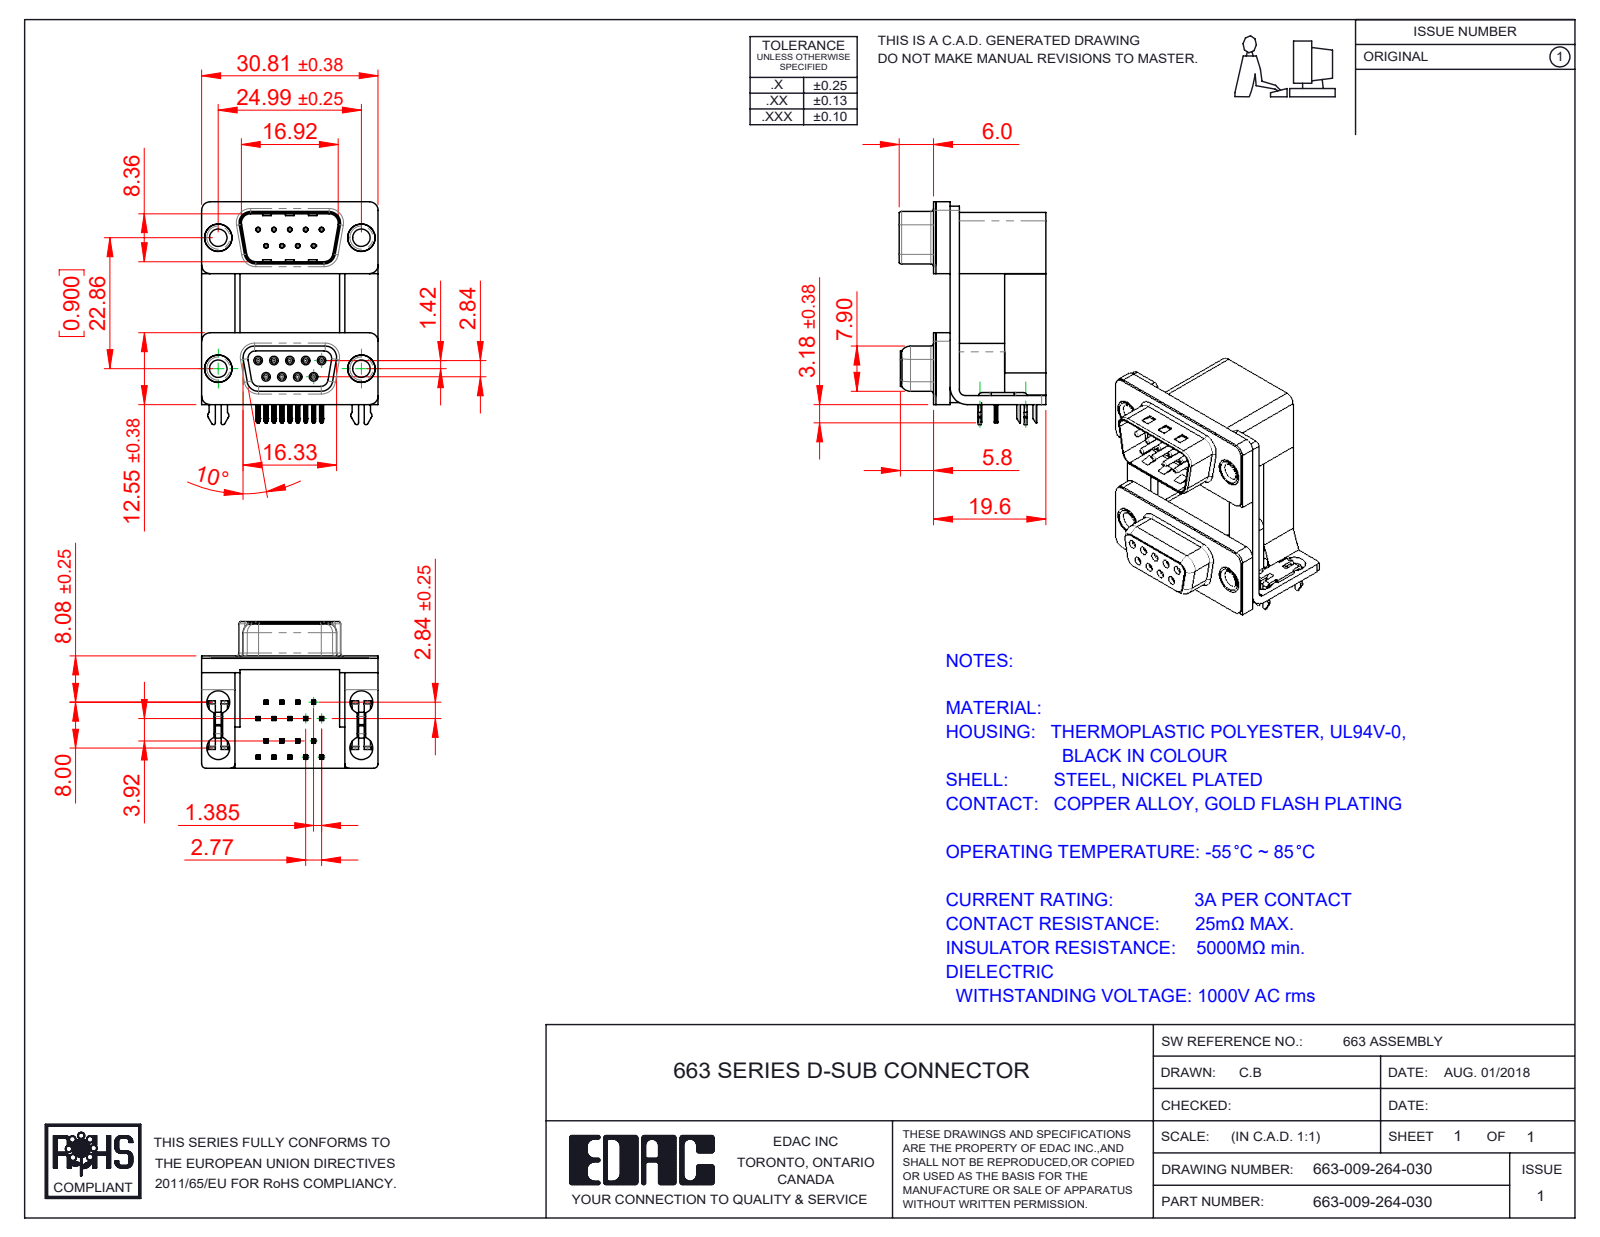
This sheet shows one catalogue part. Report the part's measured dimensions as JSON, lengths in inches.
{"part_name": "663 Contact Top Upper_H; 663-009-264-030; 663 Thru Hole Rivet; 663 Shell Plug_09 Contacts (+8 more)", "step_written_by": "SolidWorks 2020 (CONFIG_CONTROL_DESIGN)", "units": "inches", "bodies": {"solids": 31, "faces": 2597, "planar": 1365, "cylindrical": 709, "other": 523}, "overall_size": [1.532, 1.213, 1.008], "volume_in3": 0.692, "surface_area_in2": 20.46, "round_holes": [[0.031, 18], [0.014, 9], [0.035, 9], [0.157, 8], [0.12, 4], [0.138, 4], [0.189, 4], [0.197, 4]], "round_bosses_or_shafts": [[0.047, 9], [0.03, 9], [0.193, 4], [0.187, 4], [0.152, 4]], "partial_cylinders_radius": [[0.004, 74], [0.01, 46], [0.006, 36], [0.005, 18], [0.014, 18], [0.02, 16], [0.059, 15], [0.03, 10]], "face_to_face_distances": [0.098, 0.016, 0.756, 0.657, 0.472, 0.374, 0.283, 0.063, 0.488, 0.772], "hole_center_spacings": [0.124, 0.109, 0.907, 0.9, 0.218, 0.926, 0.79, 1.013]}
